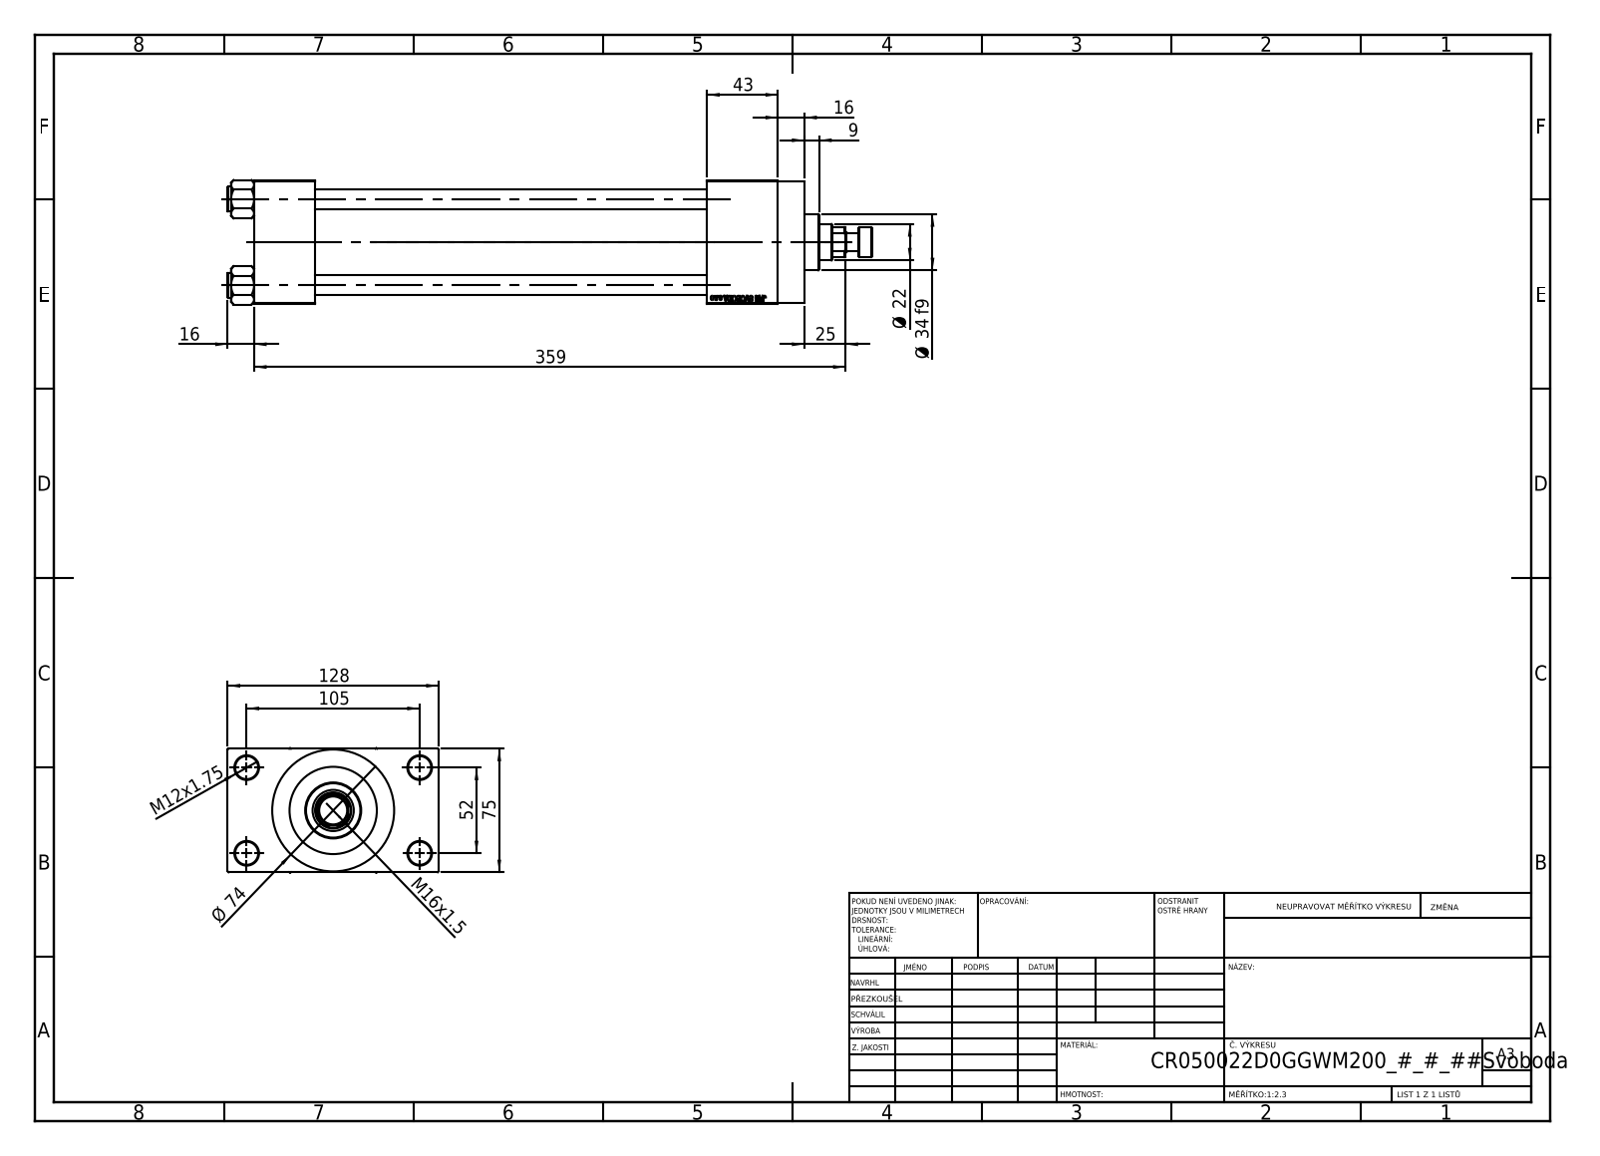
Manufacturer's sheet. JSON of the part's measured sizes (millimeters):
{"part_name": "V215CR_ROD_END_W; V215CR_D_TYCINKA; V215CR_VCP_D; V215_VC_A (+2 more)", "step_written_by": "SolidWorks 2019 (CONFIG_CONTROL_DESIGN)", "units": "millimeters", "bodies": {"solids": 12, "faces": 1118, "planar": 501, "cylindrical": 93, "other": 524}, "overall_size": [391, 128, 75.54], "volume_mm3": 1049000, "surface_area_mm2": 265752, "round_holes": [[12, 4], [14, 4], [7, 2], [20.96, 2], [30, 2], [10.5, 1], [22, 1], [25, 1], [41, 1], [50, 1], [53, 1]], "round_bosses_or_shafts": [[15, 4], [74, 1], [56, 1], [34, 1], [18, 1], [11, 1]], "partial_cylinders_radius": [[10.5, 1]], "face_to_face_distances": [75, 238, 37, 275, 26.5, 101.5, 318, 281, 43, 16], "hole_center_spacings": [26.35, 36.98, 52.3, 58.43, 58.59, 78.65, 94.37, 52]}
